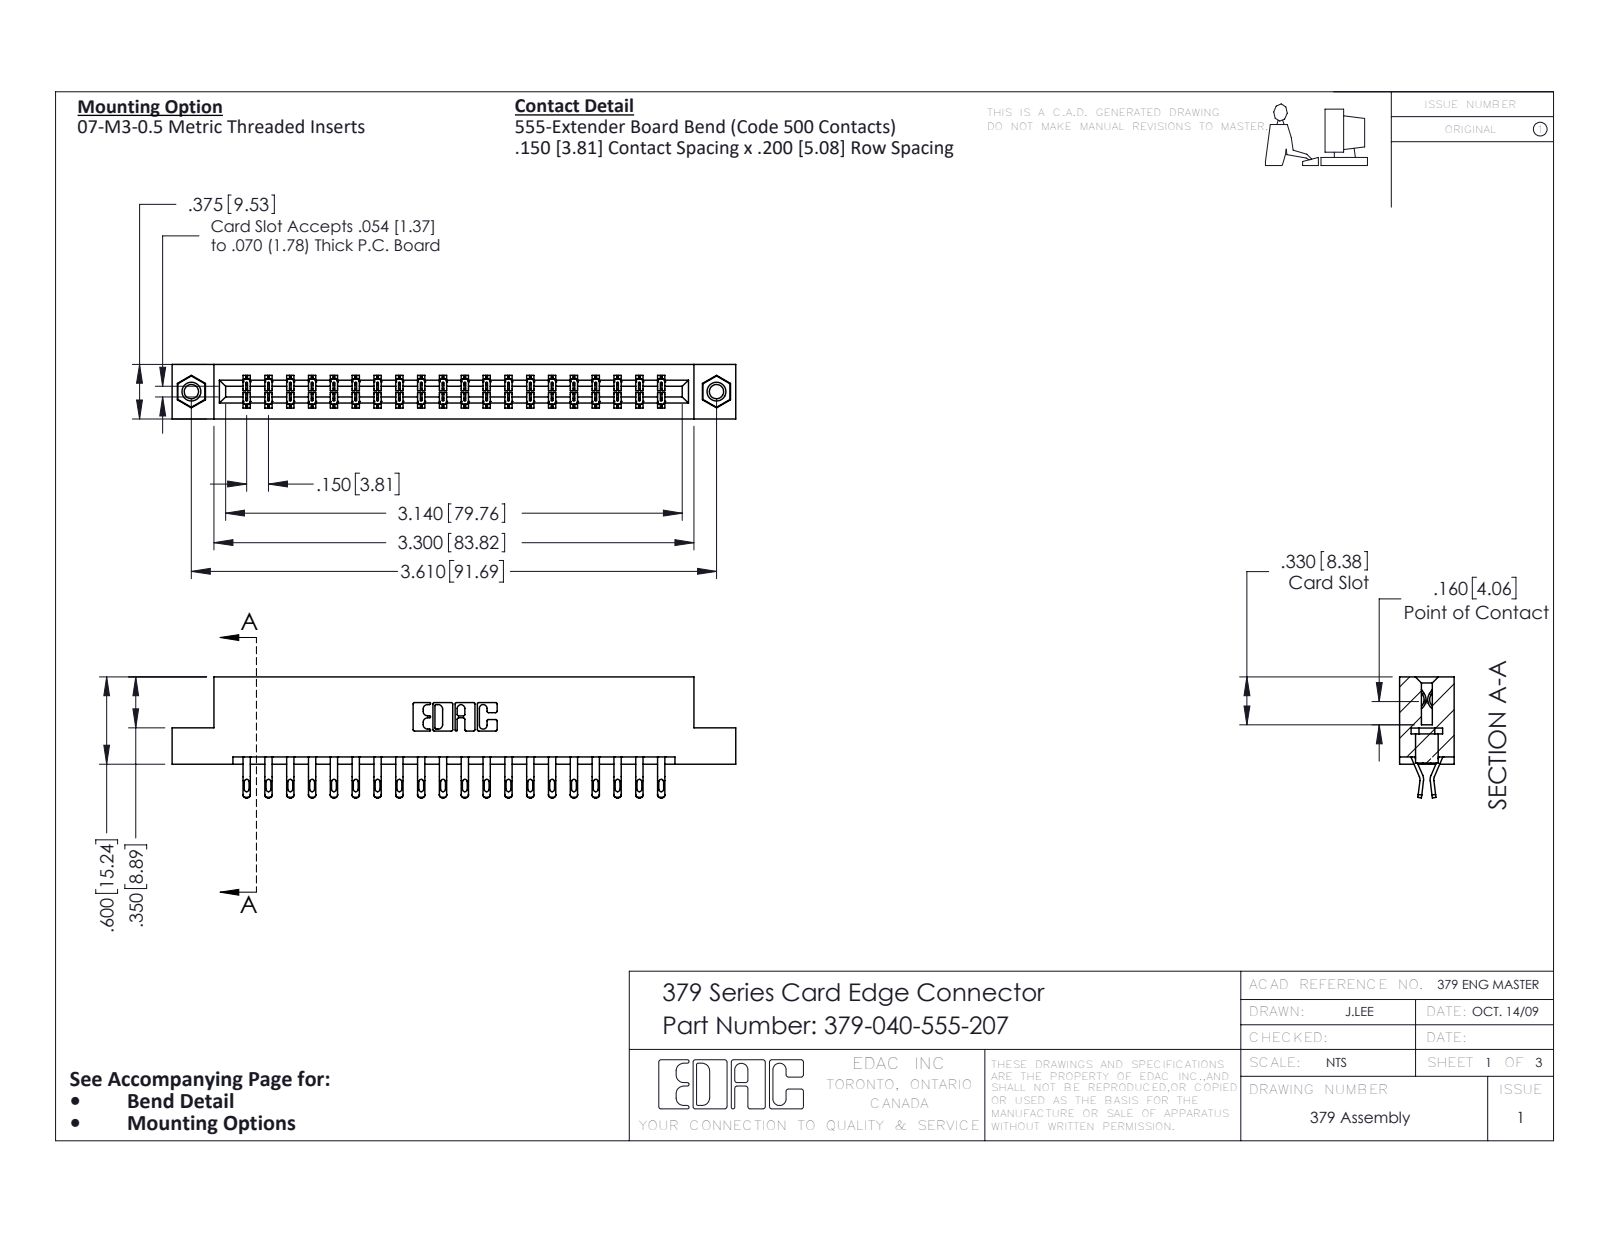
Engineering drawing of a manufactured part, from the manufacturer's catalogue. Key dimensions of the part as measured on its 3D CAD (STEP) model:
Part name (STEP PRODUCT): 379-040-555-207; 345-250-001_345-250-005-103; 345-292-001_555 Tail; 379 Part_Flush - .156 Dia - TI
STEP written by: SolidWorks 2016 (CONFIG_CONTROL_DESIGN)
Units: inches
Bodies: 43 solids, 2494 faces (1462 planar, 1016 cylindrical, 16 other)
Overall size (bounding box): 3.875 × 0.832 × 0.375
Volume: 0.629 in³ · Surface area: 18.37 in²
Round holes (diameter × count): ⌀0.098 ×2, ⌀0.125 ×2, ⌀0.156 ×2
Round bosses / shafts (diameter × count): ⌀0.155 ×2
Partial cylindrical surfaces — rounded edges, fillets, slot ends (radius × count): R0.016 ×80, R0.02 ×80, R0.006 ×60, R0.01 ×22, R0.007 ×6, R0.031 ×6, R0.026 ×3, R0.01 ×2
Main face-to-face distances: 0.3, 0.075, 0.375, 0.2, 0.1, 0.15, 0.05, 0.225, 0.6, 0.55
Hole centre spacings: 3.61
